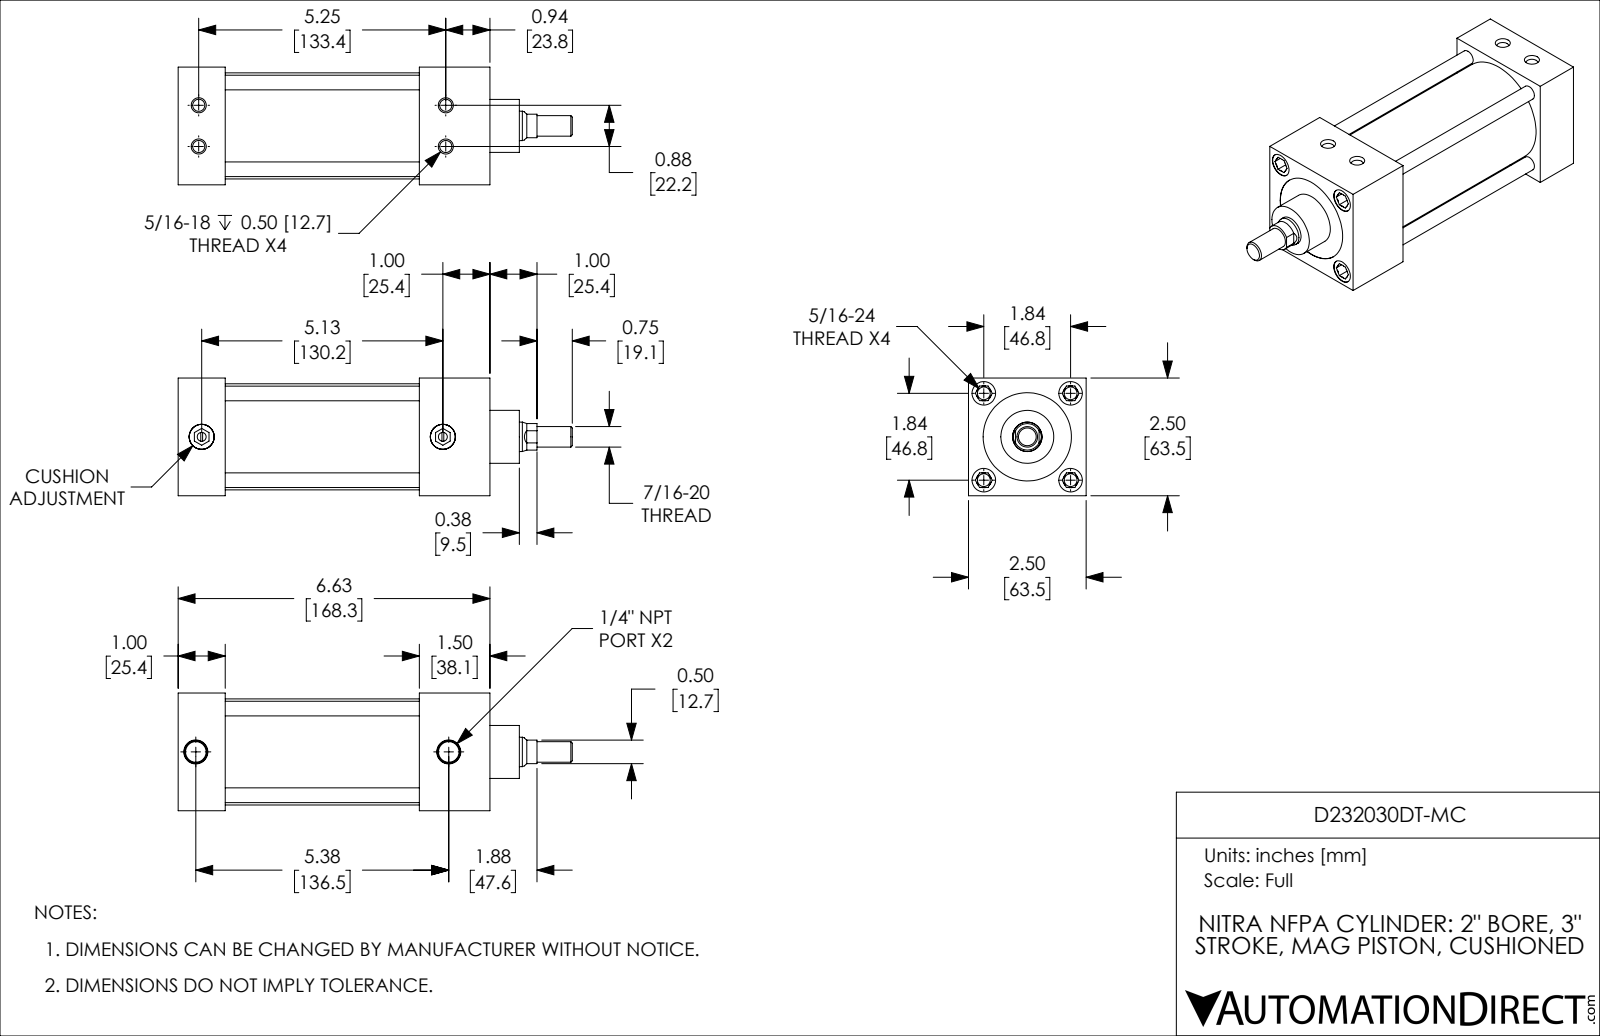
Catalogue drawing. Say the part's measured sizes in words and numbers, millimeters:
The part is named "D232030DT-MC_PISTON_KK1; D232030DT-MC_BODY; D232030DT-MC_CUSHION; D232030DT-MC". Its 3-D file was written by "SolidWorks 2019 (CONFIG_CONTROL_DESIGN)". It is 4 solids with 248 faces: 90 planar, 78 cylindrical and 80 other. Overall it measures 212.7 by 63.5 by 63.5 millimeters. Its volume is 405 700 cubic millimeters and its surface area 104 300 square millimeters. Round holes: 7 of diameter 6.9, 4 of diameter 6.5, 4 of diameter 12.7, 2 of diameter 4.8, 2 of diameter 11.1, 2 of diameter 13.5, 1 of diameter 15.9, 1 of diameter 47.6, 1 of diameter 50.8. Round bosses or shafts: 4 of diameter 7.9, 2 of diameter 13.5, 1 of diameter 57.2, 1 of diameter 50.8, 1 of diameter 28.6, 1 of diameter 15.8, 1 of diameter 11.1. Partial cylindrical surfaces (rounded edges, fillets, slot ends): 1 of radius 7.1. The main face-to-face distances are 63.5, 25.4, 130.2, 104.8, 28.6, 54, 76.2, 38.1, 168.3, 142.9. The hole center spacings are 46.7, 46.8, 33, 11.2, 11.3, 22.2, 33.1, 66.1.
